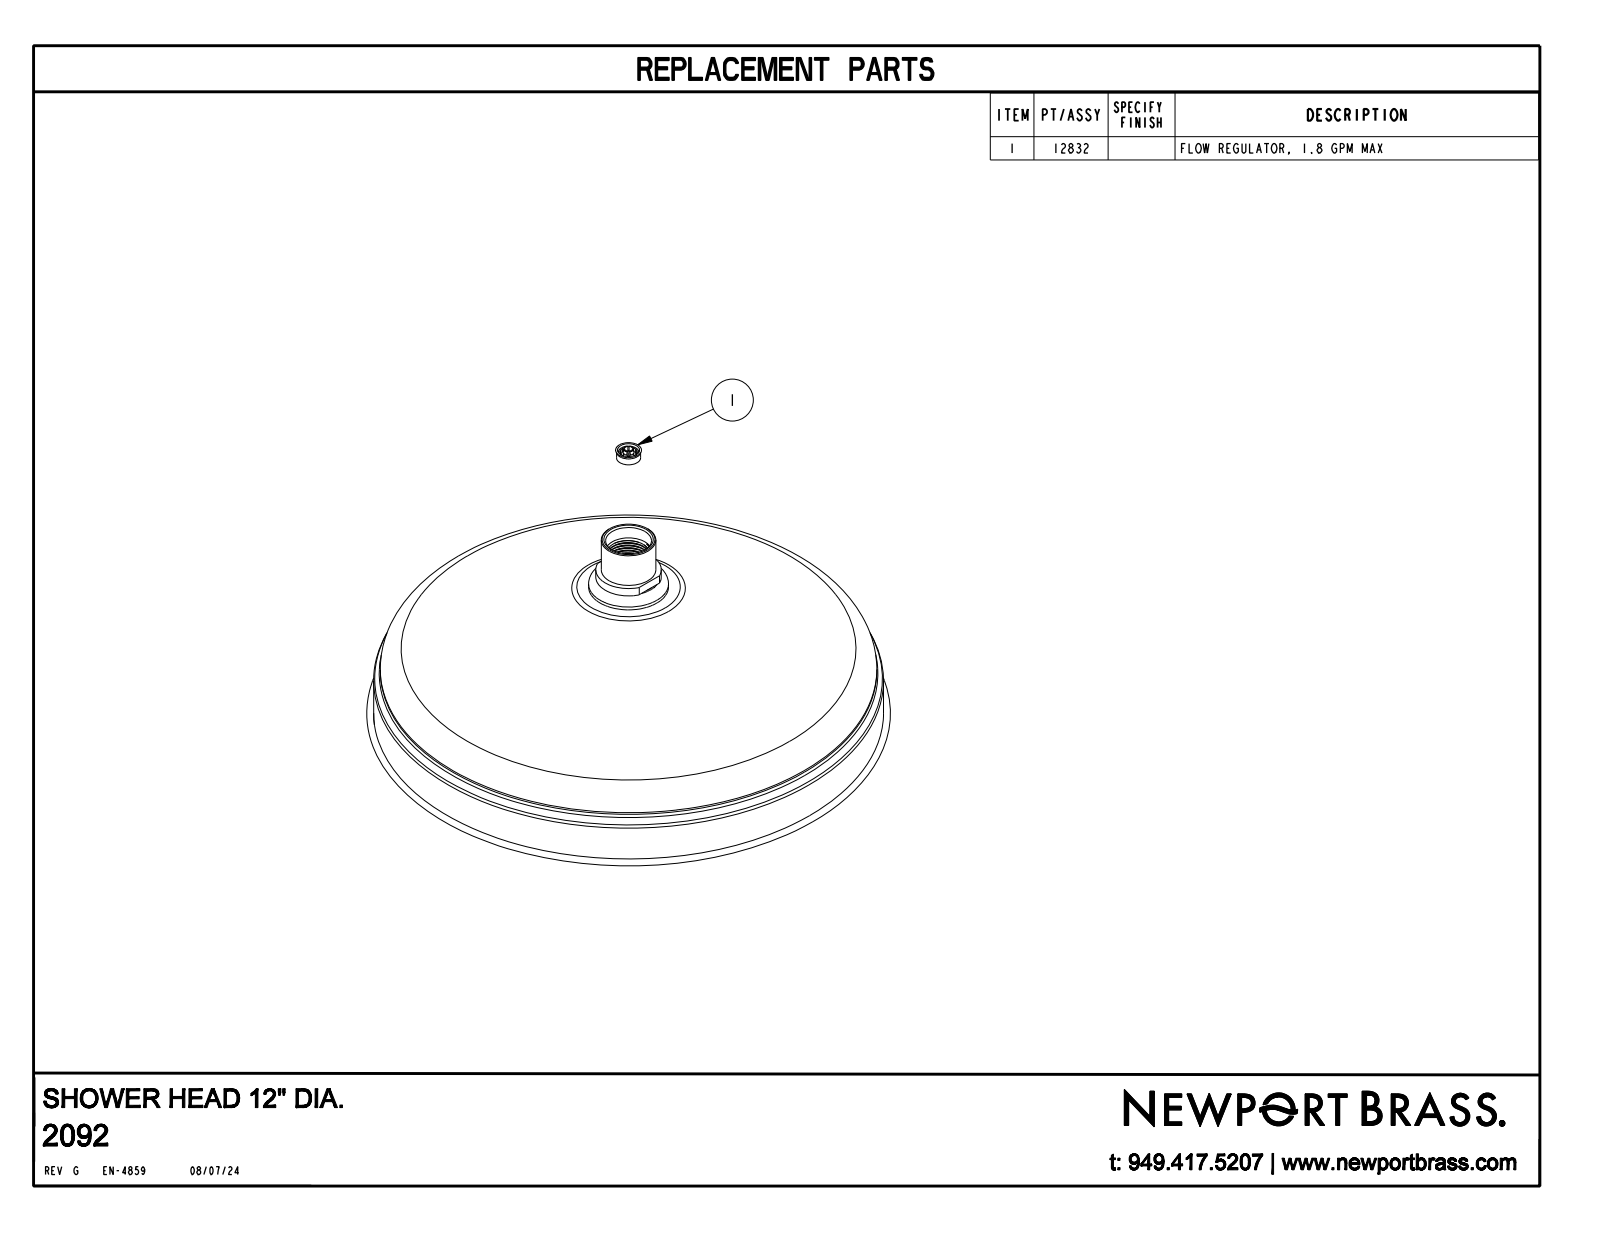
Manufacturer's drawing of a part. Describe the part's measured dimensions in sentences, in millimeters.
The part is named "2092". Its 3-D file was written by "CREO PARAMETRIC BY PTC INC, 2018400 (AUTOMOTIVE_DESIGN)". It is 1 solid with 1079 faces: 21 planar, 292 cylindrical and 766 other. Overall it measures 304.8 by 304.8 by 125.8 millimeters. Its volume is 354 600 cubic millimeters and its surface area 532 100 square millimeters. Round holes: 127 of diameter 1.2, 1 of diameter 37.8, 1 of diameter 254, 1 of diameter 286, 1 of diameter 286.6, 1 of diameter 287, 1 of diameter 294.8. Round bosses or shafts: 1 of diameter 296.8, 1 of diameter 292, 1 of diameter 289, 1 of diameter 256, 1 of diameter 46.5, 1 of diameter 44, 1 of diameter 40, 1 of diameter 39.7. Partial cylindrical surfaces (rounded edges, fillets, slot ends): 1 of radius 19.1. The main face-to-face distances are 1, 1.5, 0.5, 2.5, 61.5, 60, 75.2, 76.7, 15.2, 60.5. The hole center spacings are 81.2, 128.8, 140.6, 161, 42, 114.8, 21.2, 62.2.
